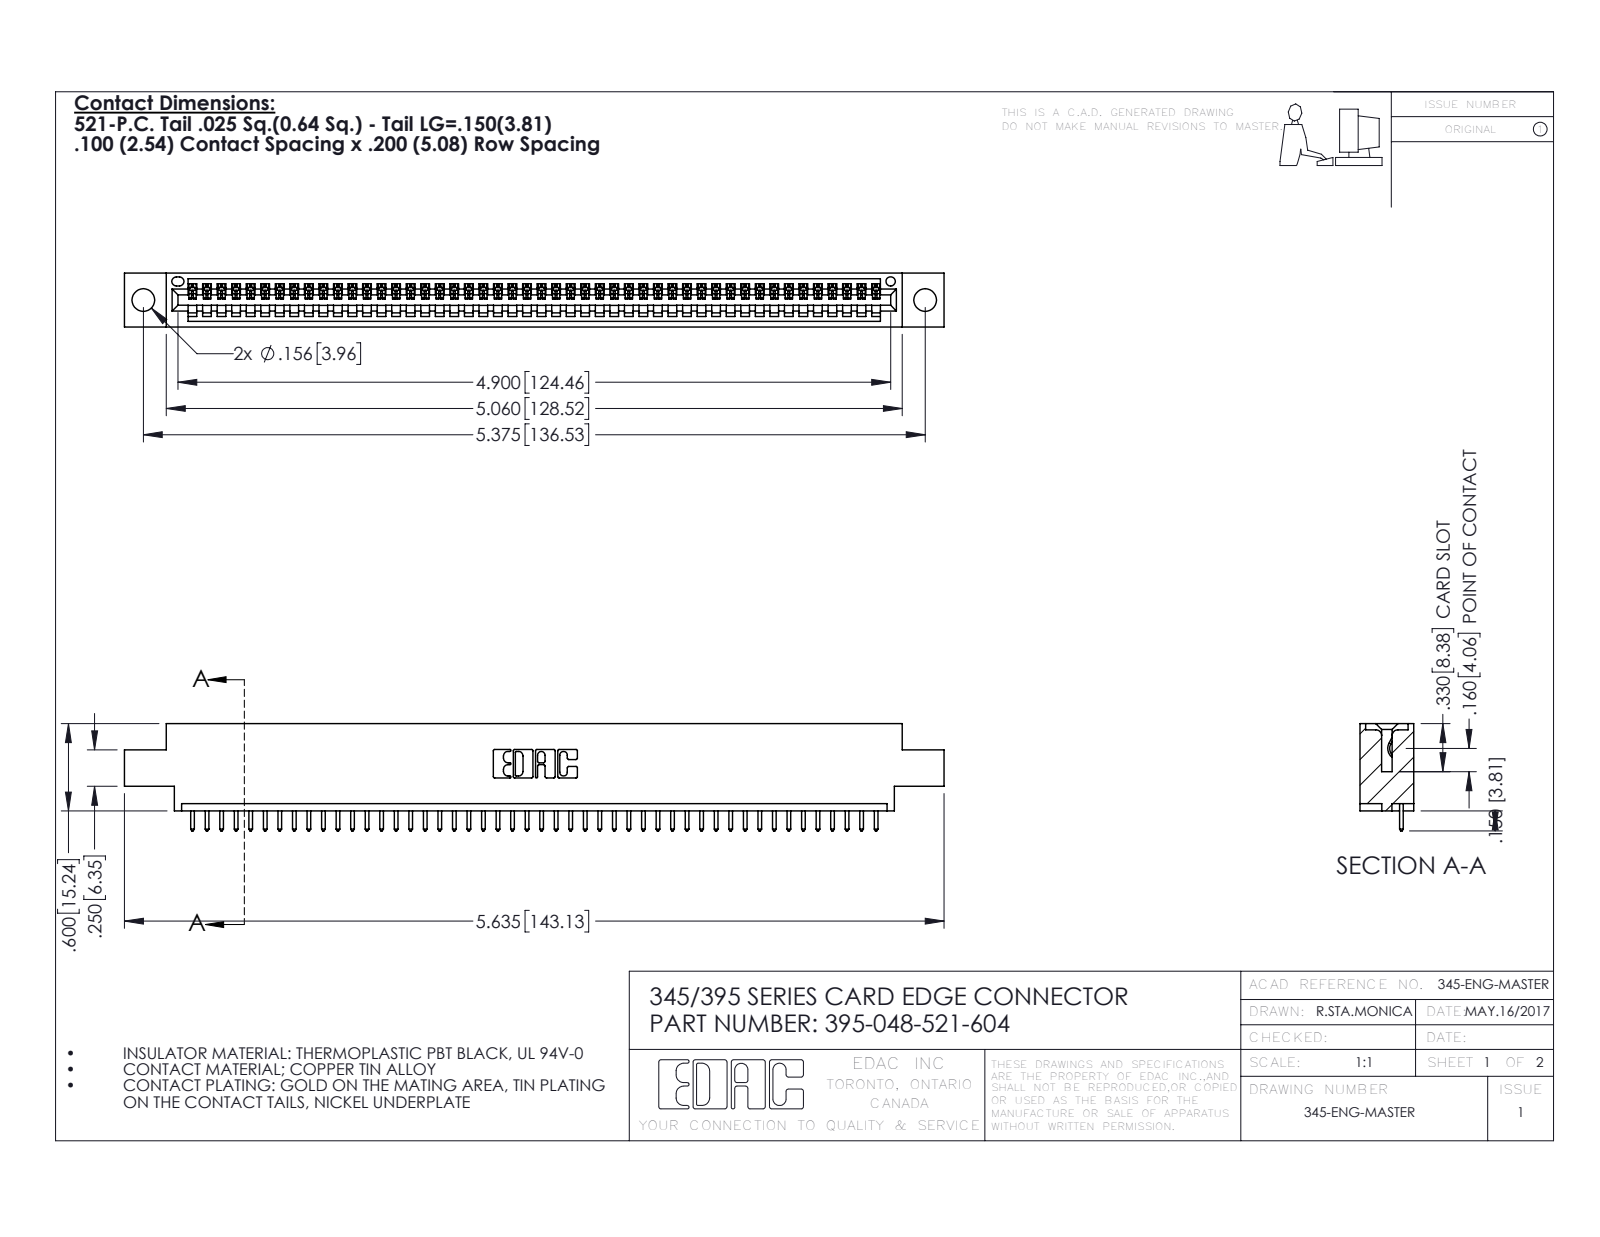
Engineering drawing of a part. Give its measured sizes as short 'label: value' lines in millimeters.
name: 345 Part_0.170 Offset - 0.156 Dia-TH; 395-048-521-604; 345-292-001_345-293-121
written by: SolidWorks 2016 (CONFIG_CONTROL_DESIGN)
unit: mm
bodies: 49 solids, 2914 faces (2004 planar, 910 cylindrical, 0 other)
size: 143.1 × 18.7 × 9.4
volume: 13 300 mm³; area: 17 170 mm²
holes: 2× ⌀4, 1× ⌀1.6
rounds: 96× R0.2, 96× R0.3, 22× R0.3, 6× R0.2, 6× R0.8, 3× R0.7, 2× R0.8, 2× R1
face distances: 7.6, 1.8, 9.4, 5.1, 2.5, 6.9, 0.6, 5.7, 4.4, 3.8
hole spacings: 6.9, 130.5, 136.5
